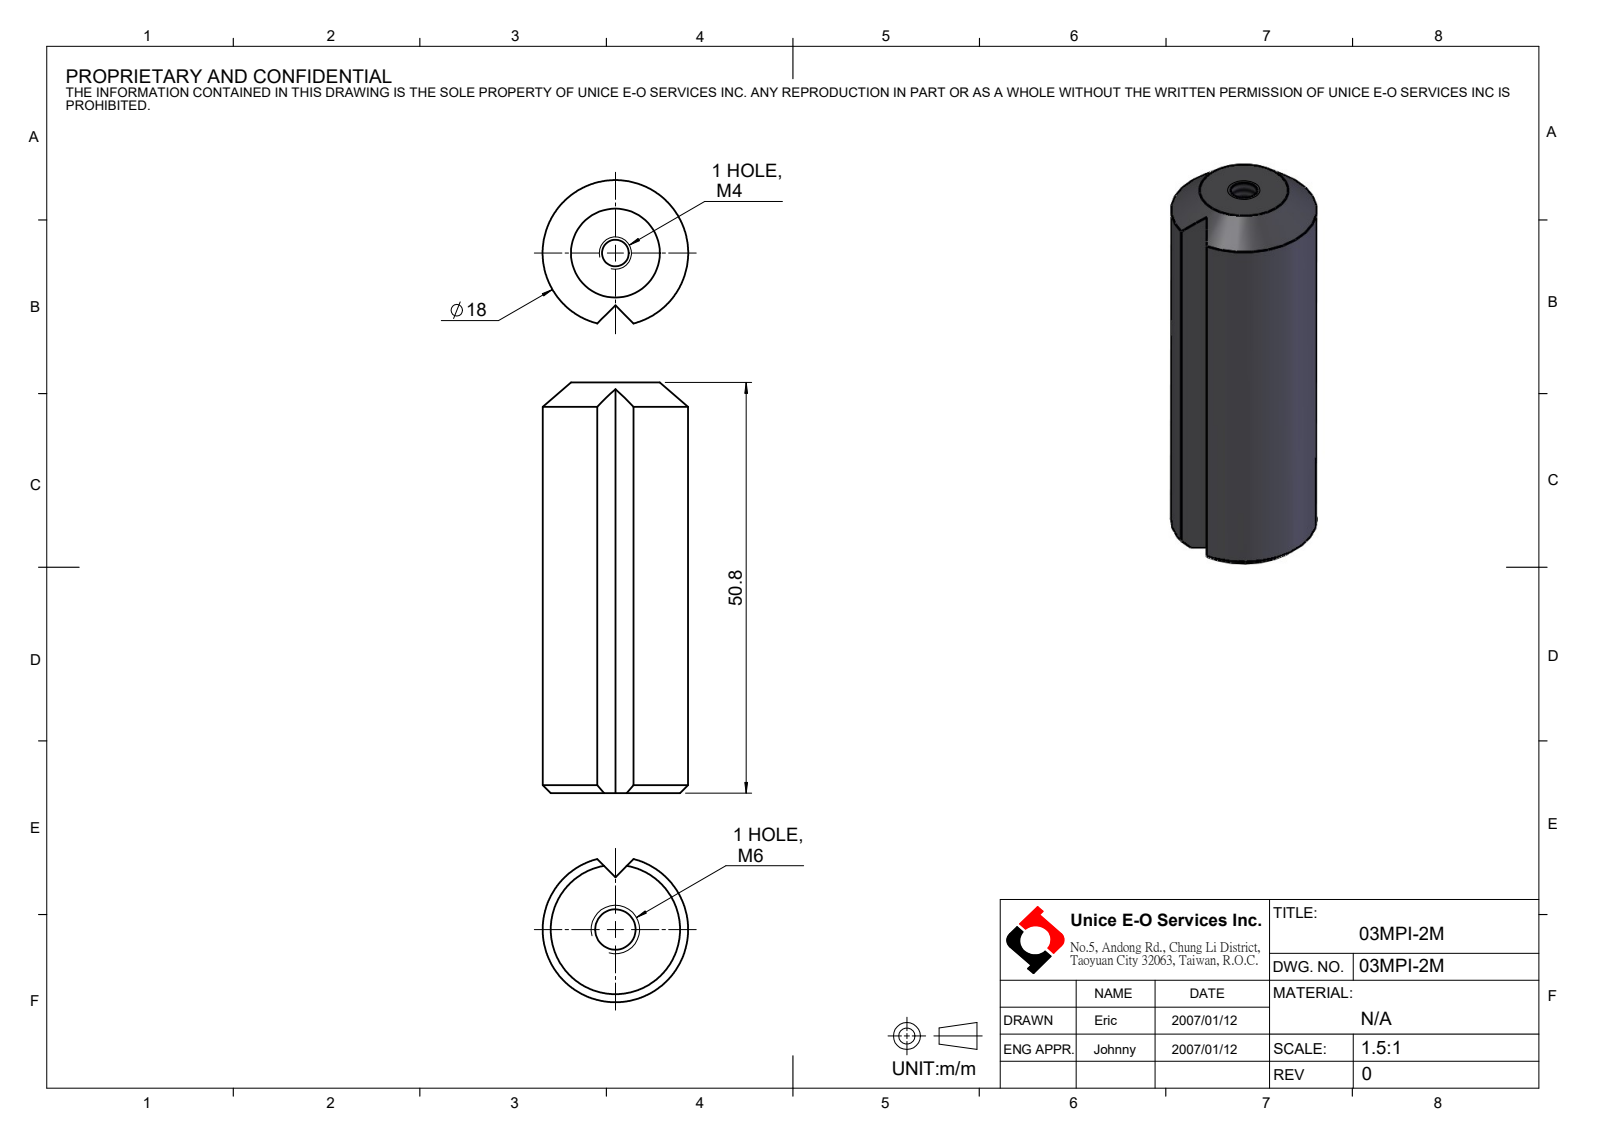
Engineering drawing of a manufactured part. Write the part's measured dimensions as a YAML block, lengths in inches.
part_name: "03MPI-2M"
step_written_by: "SolidWorks 2016 (CONFIG_CONTROL_DESIGN)"
units: inches
bodies: {solids: 1, faces: 20, planar: 4, cylindrical: 7, other: 9}
overall_size: [2, 0.709, 0.697]
volume: 0.73
surface_area: 5.665
round_holes:
  - {diameter: 0.13, count: 1}
  - {diameter: 0.197, count: 1}
round_bosses_or_shafts:
  - {diameter: 0.709, count: 1}
face_to_face_distances: [2]
